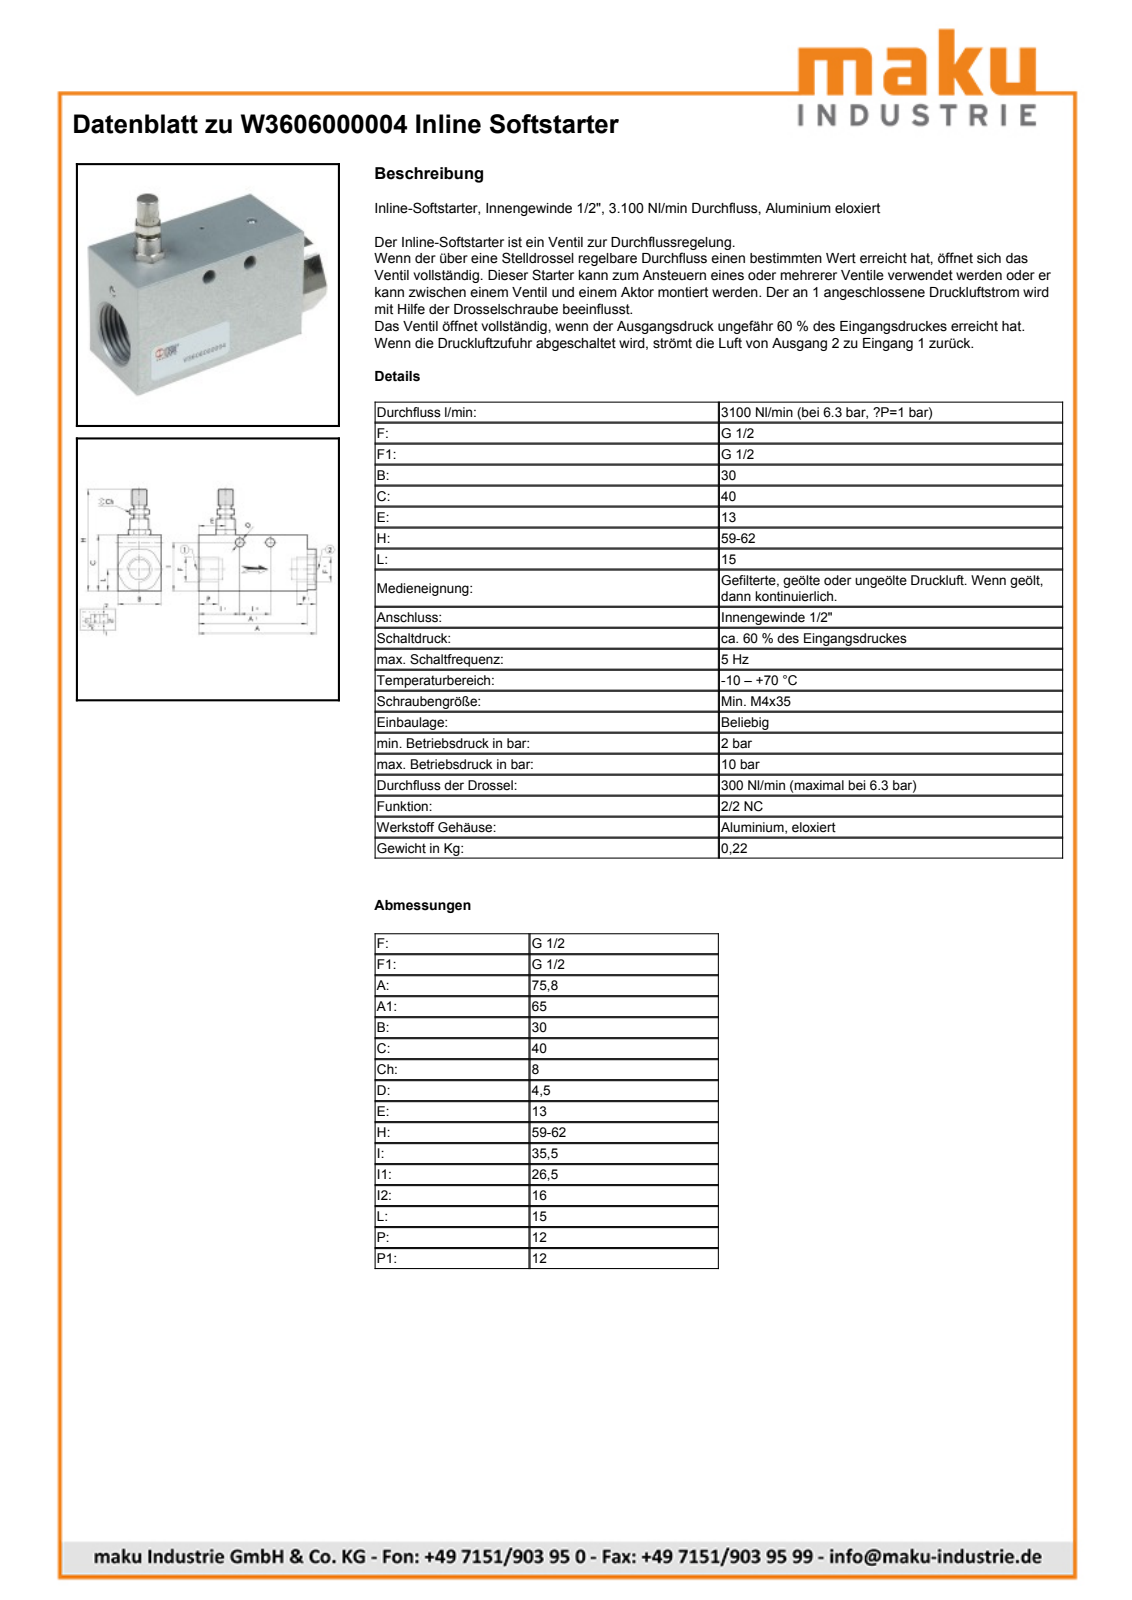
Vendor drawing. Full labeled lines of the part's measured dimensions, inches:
Part name (STEP PRODUCT): W360600000459
STEP written by: PARTsolutions (AUTOMOTIVE_DESIGN)
Units: inches
Bodies: 1 solid, 61 faces (33 planar, 26 cylindrical, 2 other)
Overall size (bounding box): 2.984 × 2.323 × 1.181
Volume: 4.693 in³ · Surface area: 23.84 in²
Round holes (diameter × count): ⌀0.177 ×2, ⌀0.733 ×1
Round bosses / shafts (diameter × count): ⌀0.335 ×1, ⌀0.272 ×1, ⌀0.197 ×1
Partial cylindrical surfaces — rounded edges, fillets, slot ends (radius × count): R0.177 ×1, R0.201 ×1, R0.573 ×1
Main face-to-face distances: 1.181, 1.575, 2.559, 0.551, 2.433, 1.063, 2.008, 2.984, 0.425, 1.882
Hole centre spacings: 0.63
